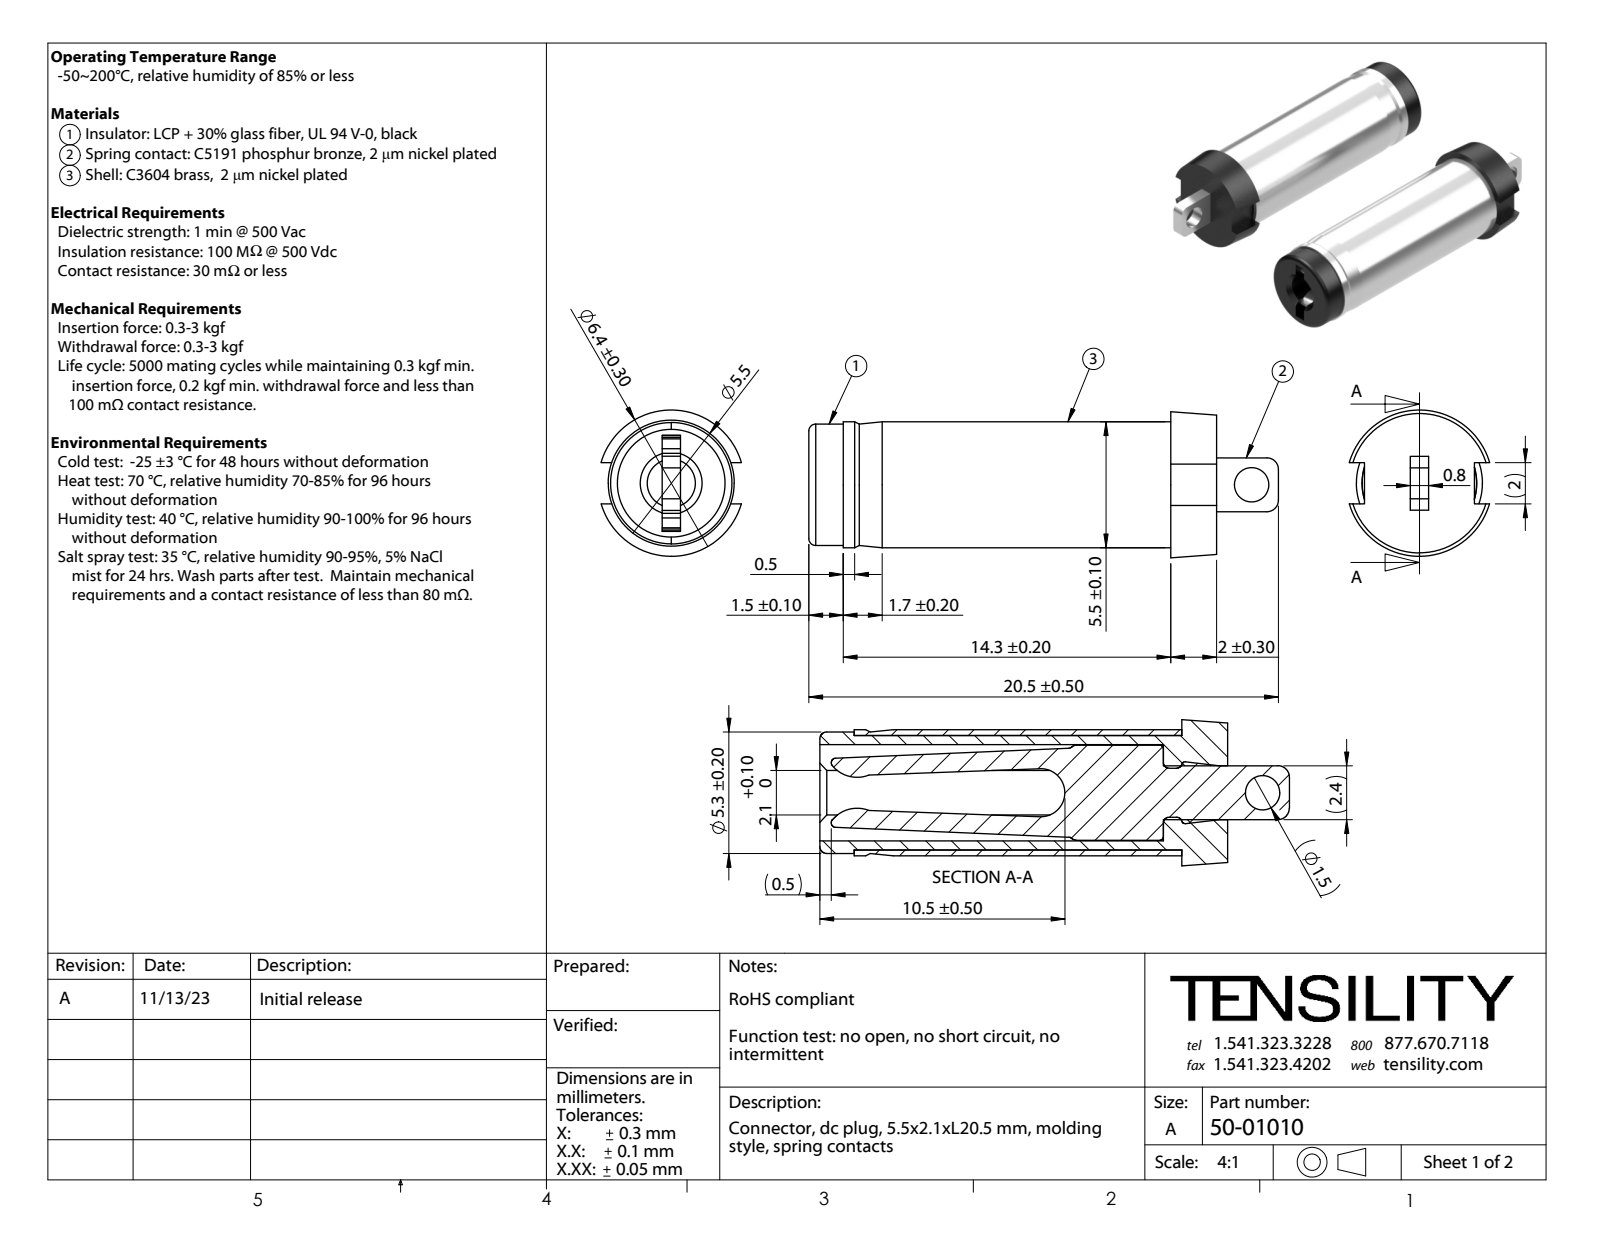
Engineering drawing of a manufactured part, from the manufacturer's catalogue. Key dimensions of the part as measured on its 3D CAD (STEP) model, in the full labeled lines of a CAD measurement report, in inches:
Part name (STEP PRODUCT): 1CP00.STEP; DT521-107-1A.STEP; 50-01010.STEP; JV551-143.STEP (+1 more)
STEP written by: SolidWorks 2021 (CONFIG_CONTROL_DESIGN)
Units: inches
Bodies: 3 solids, 88 faces (42 planar, 35 cylindrical, 11 other)
Overall size (bounding box): 0.807 × 0.251 × 0.241
Volume: 0.023 in³ · Surface area: 1.798 in²
Round holes (diameter × count): ⌀0.059 ×1, ⌀0.197 ×1
Round bosses / shafts (diameter × count): ⌀0.217 ×1, ⌀0.209 ×1
Partial cylindrical surfaces — rounded edges, fillets, slot ends (radius × count): R0.006 ×4, R0.008 ×4, R0.01 ×4, R0.012 ×2, R0.02 ×2, R0.041 ×2, R0.056 ×2
Main face-to-face distances: 0.031, 0.079, 0.165, 0.11, 0.622, 0.701, 0.059, 0.563, 0.642, 0.035
